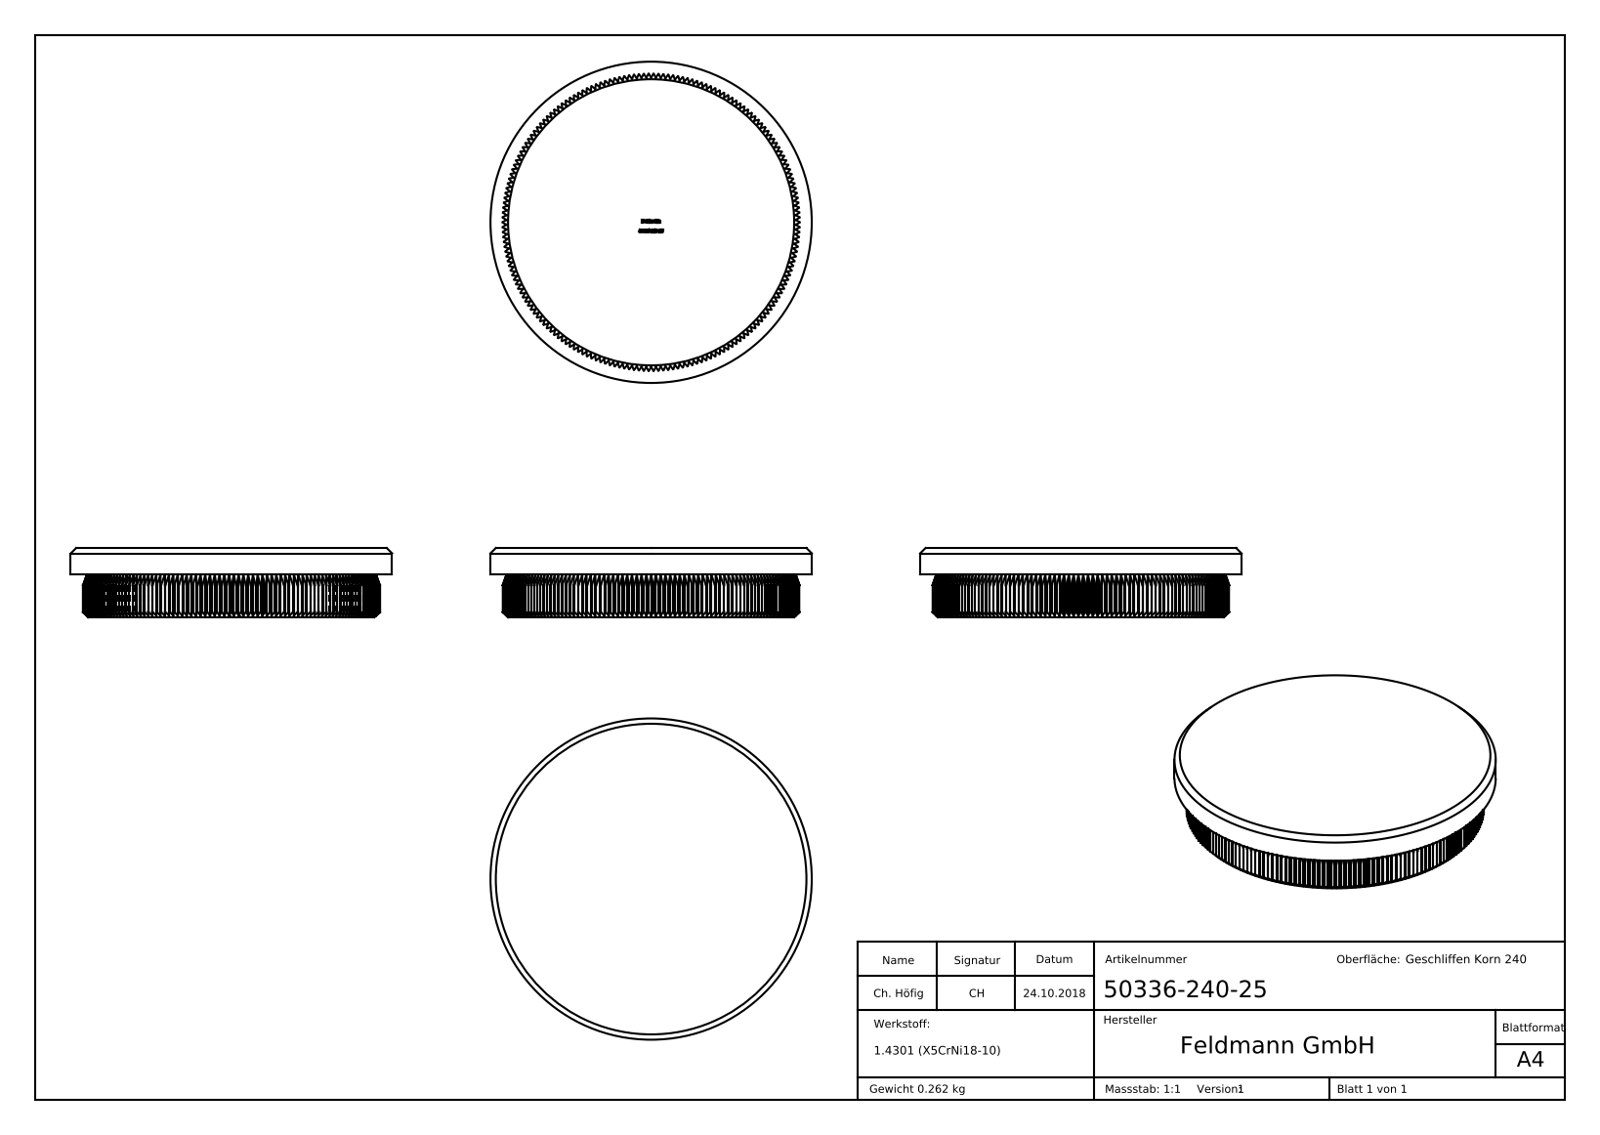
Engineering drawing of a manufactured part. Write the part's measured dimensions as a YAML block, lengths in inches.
part_name: "50336-240-25"
step_written_by: "SolidWorks 2015 (CONFIG_CONTROL_DESIGN)"
units: inches
bodies: {solids: 1, faces: 1035, planar: 518, cylindrical: 192, other: 325}
overall_size: [2.374, 2.374, 0.512]
volume: 2.023
surface_area: 13.83
round_bosses_or_shafts:
  - {diameter: 2.374, count: 1}
partial_cylinders:
  - {radius: 1.096, count: 1}
face_to_face_distances: [0.512, 0.315, 0.197, 1.069, 1.069, 1.068, 1.07, 0.311, 0.508, 0.026]
